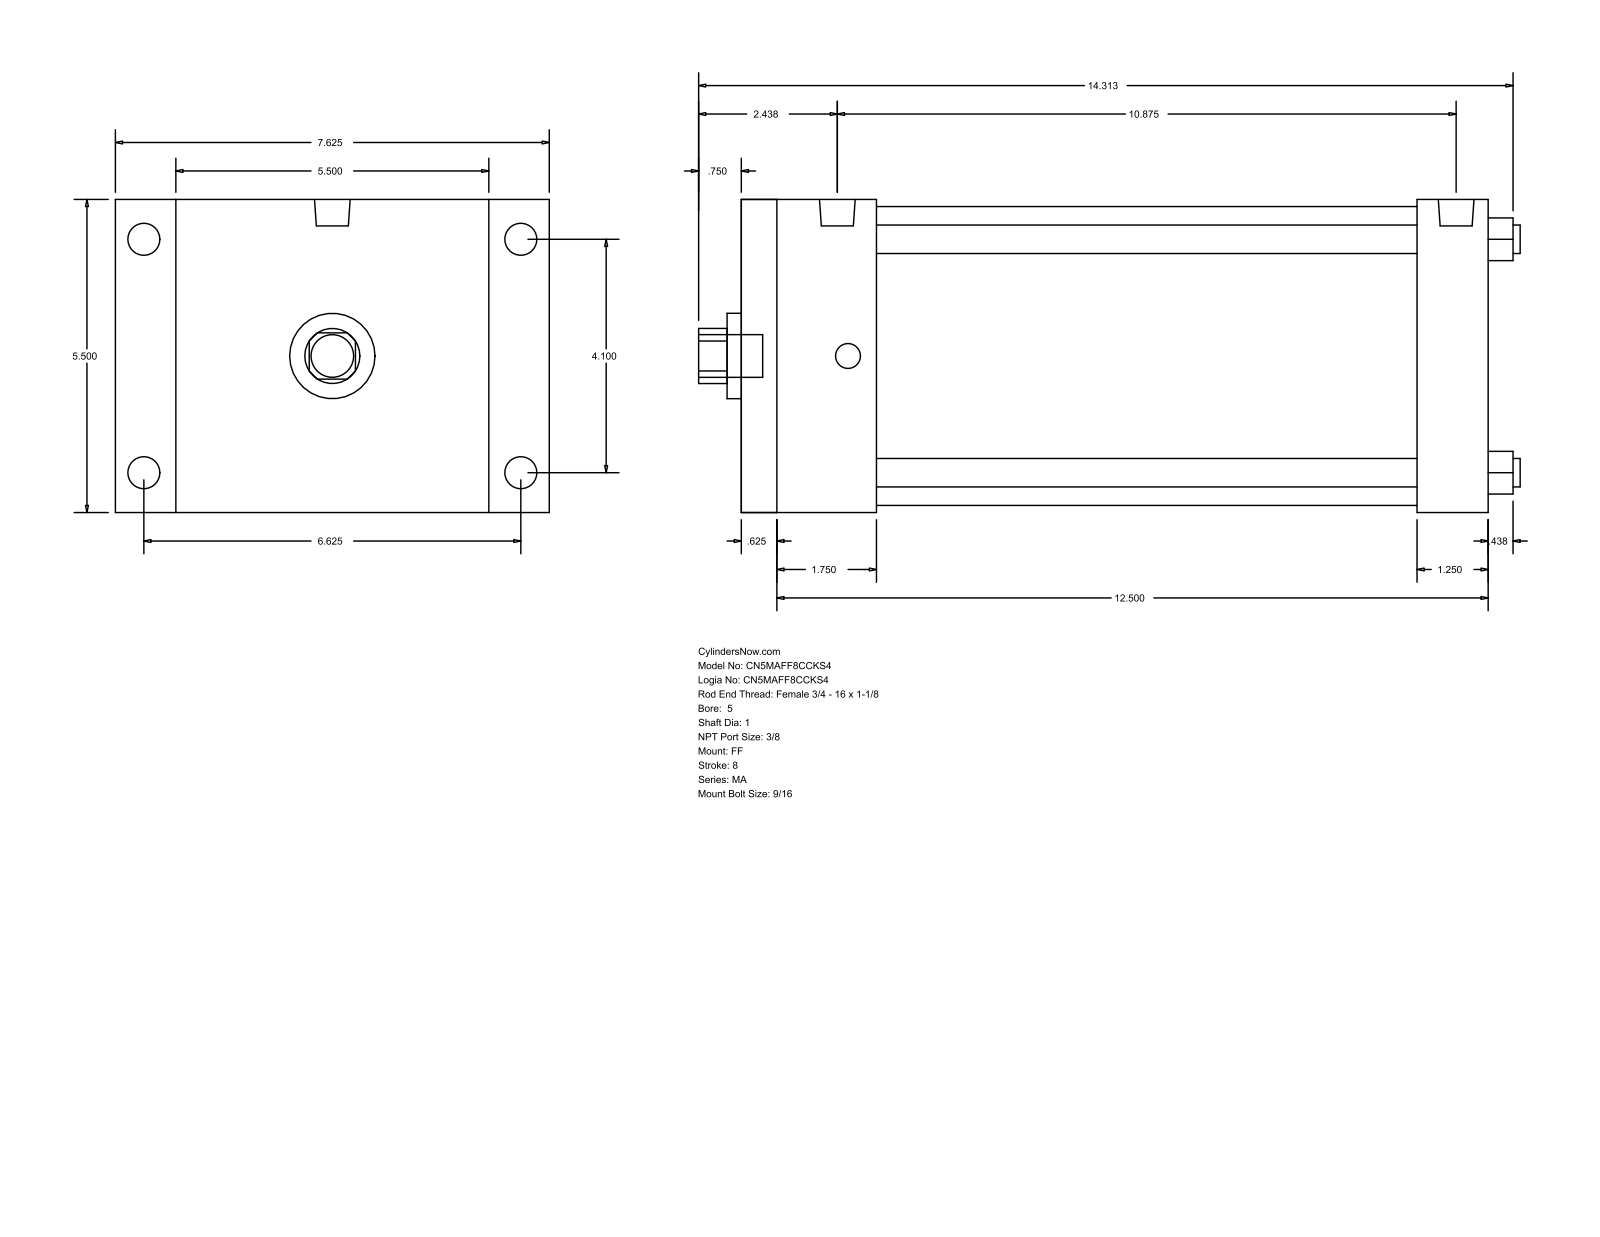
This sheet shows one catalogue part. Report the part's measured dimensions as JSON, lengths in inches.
{"part_name": "MA_FF__0500_1", "step_written_by": "GSSL Pune (CONFIG_CONTROL_DESIGN)", "units": "inches", "bodies": {"solids": 0, "faces": 92, "planar": 64, "cylindrical": 28, "other": 0}, "overall_size": [14.437, 7.625, 5.5], "round_holes": [[0.5, 4], [1, 1], [1.5, 1], [5.25, 1]], "round_bosses_or_shafts": [[0.563, 4], [0.437, 4], [0.627, 2], [0.75, 1]], "partial_cylinders_radius": [[0.484, 1]], "face_to_face_distances": [5.5, 13.125, 0.625, 12.5, 11.875, 11.25, 1.25, 2.375, 1.75, 9.5], "hole_center_spacings": [2.899, 4.1, 5.798]}
